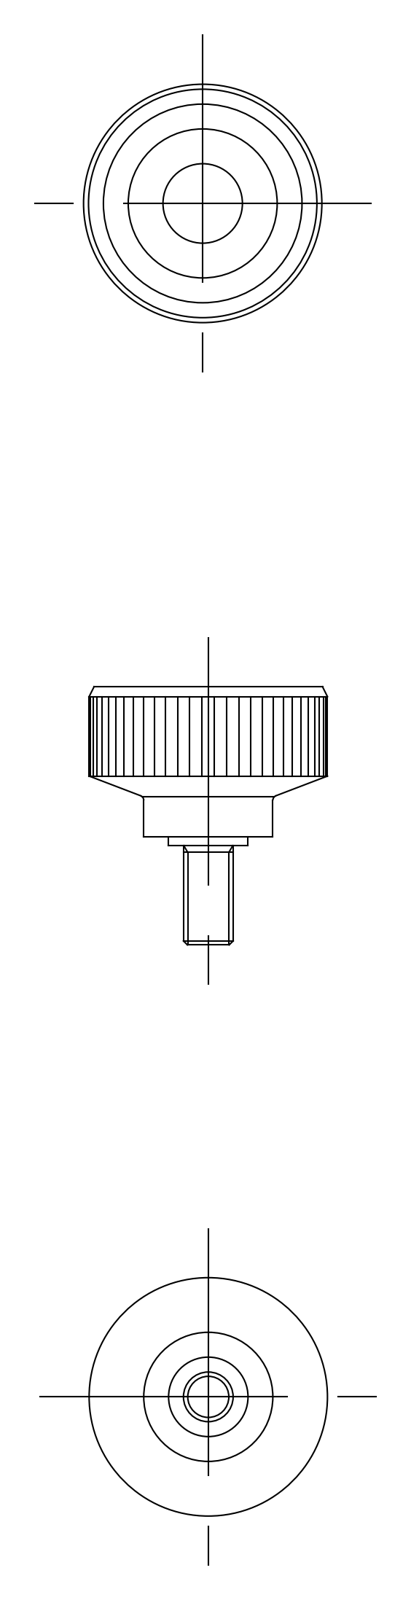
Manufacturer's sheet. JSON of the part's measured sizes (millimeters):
{"part_name": "screw; knob; KKM_24_M5_10_5149_36", "step_written_by": "CADfix (AUTOMOTIVE_DESIGN)", "units": "millimeters", "bodies": {"solids": 2, "faces": 35, "planar": 0, "cylindrical": 0, "other": 35}, "overall_size": [26, 24, 24], "volume_mm3": 3866, "surface_area_mm2": 2580}
